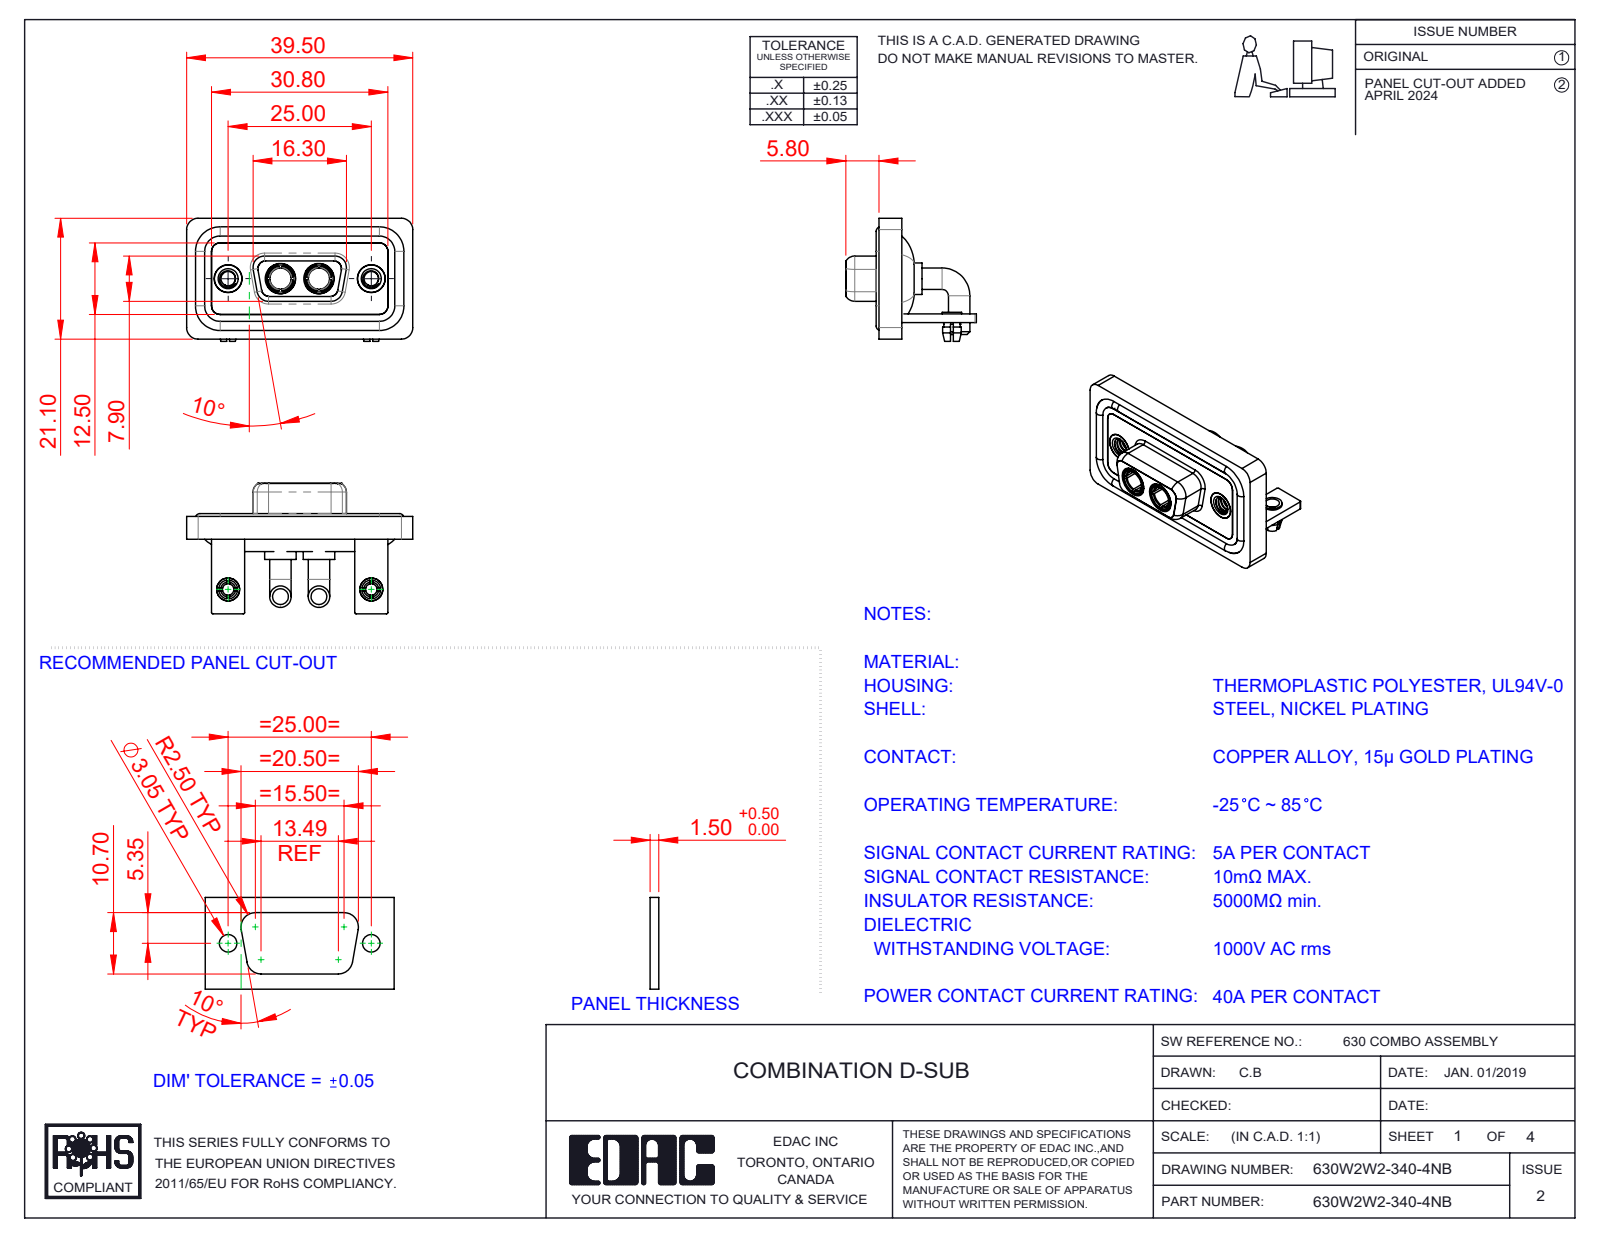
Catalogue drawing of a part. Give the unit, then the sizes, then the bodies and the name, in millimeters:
Units: millimetres
Overall size (bounding box): 39.5 × 22.8 × 21.5
Round holes (diameter × count): ⌀2.5 ×4, ⌀4.85 ×4, ⌀2 ×2, ⌀3.2 ×2, ⌀3.7 ×2, ⌀4 ×2, ⌀4.05 ×2, ⌀5 ×2, ⌀5.3 ×2
Round bosses / shafts (diameter × count): ⌀3.75 ×4, ⌀1.6 ×4, ⌀5.5 ×2, ⌀5.2 ×2, ⌀4.96 ×2, ⌀4.95 ×2, ⌀4.8 ×2, ⌀4.75 ×2
Partial cylindrical surfaces — rounded edges, fillets, slot ends (radius × count): R2 ×19, R1.5 ×18, R0.25 ×16, R1.35 ×8, R1.6 ×8, R0.5 ×5, R0.6 ×4, R0.65 ×4
Main face-to-face distances: 0.4, 2.9, 1.5, 1.8, 1.1, 3.7, 0.8, 2.5, 1.6, 3.1
Hole centre spacings: 9.14, 15.86, 25, 6.72
Volume: 5 357 mm³ · Surface area: 8 822 mm²
Bodies: 15 solids, 676 faces (231 planar, 292 cylindrical, 153 other)
Part name (STEP PRODUCT): 630W2W2-340-4NB; 630Combo Stabilizer Bracket_50 Contacts; 630Combo Threaded Rivet_A; 630Combo Shell Front_09 Contacts (+5 more)
STEP written by: SolidWorks 2023 (CONFIG_CONTROL_DESIGN)
